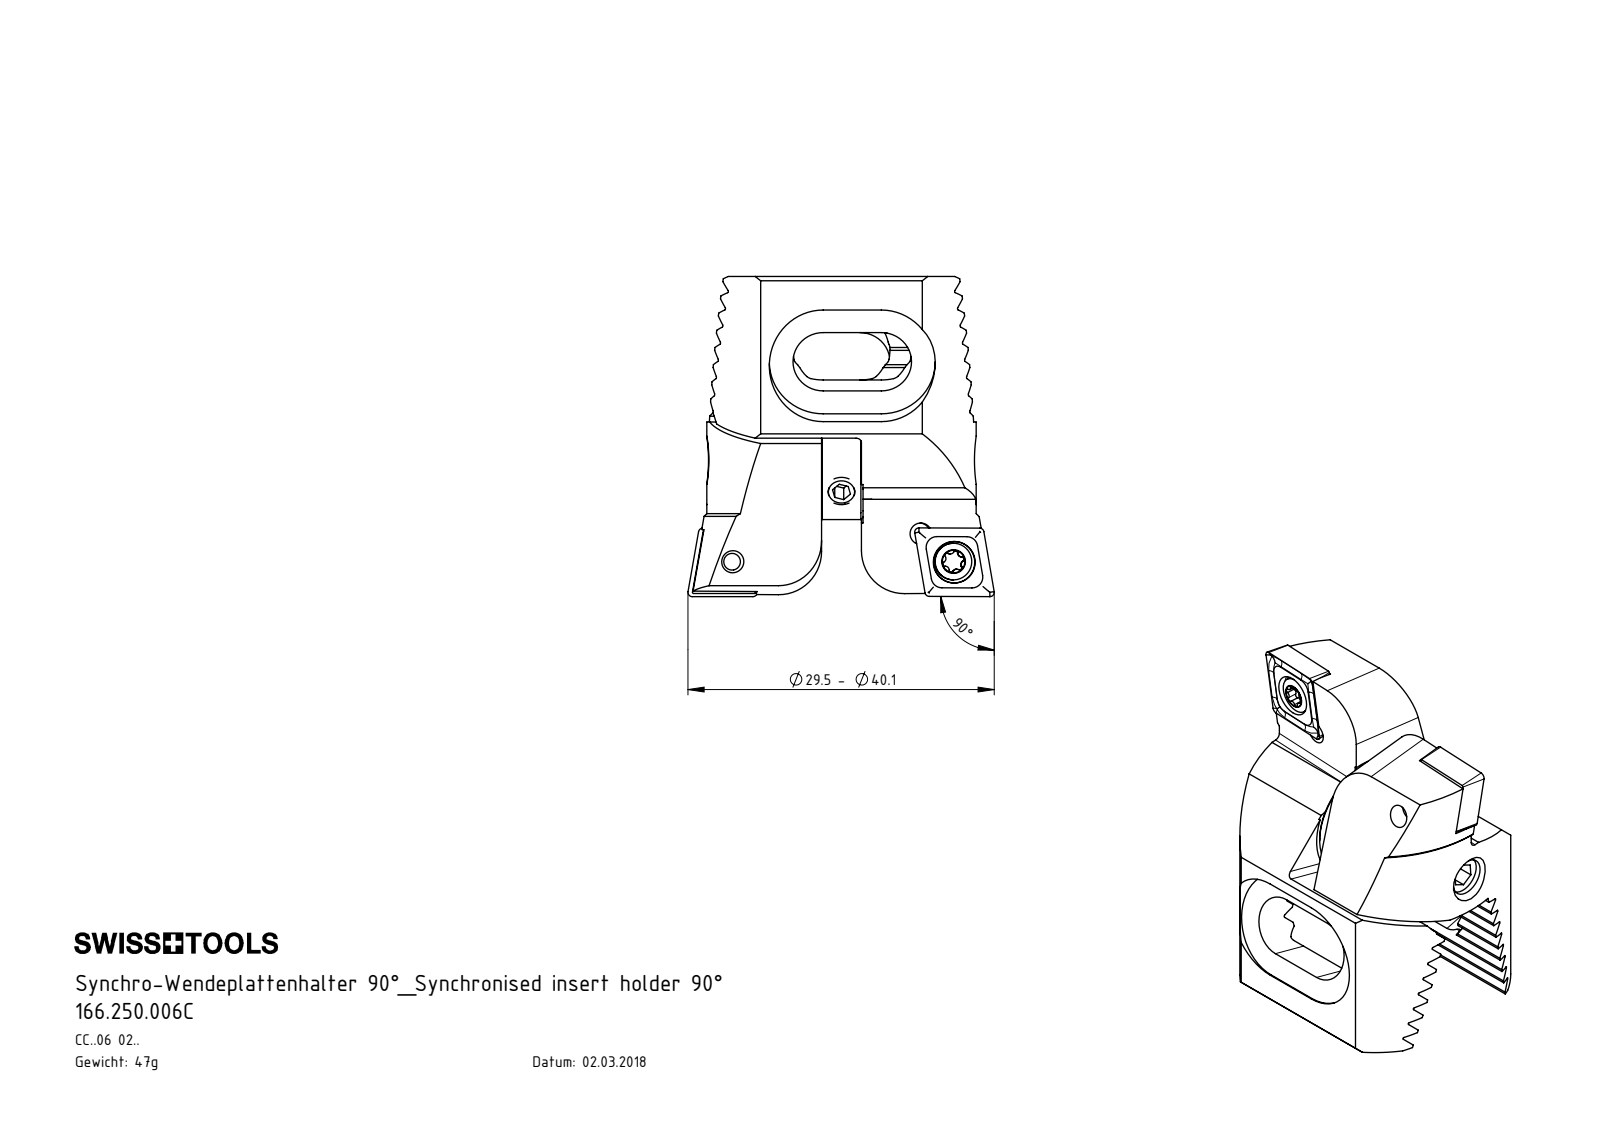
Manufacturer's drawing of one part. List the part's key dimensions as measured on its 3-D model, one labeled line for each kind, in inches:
Part name (STEP PRODUCT): ISO 4026 - M3 x 3; WCA-ER2.001.006_A; Z25-WCA.001.016_A; CCMT060204 (+4 more)
STEP written by: SolidWorks 2017 (CONFIG_CONTROL_DESIGN)
Units: inches
Bodies: 11 solids, 517 faces (205 planar, 172 cylindrical, 140 other)
Overall size (bounding box): 1.169 × 1.119 × 0.795
Volume: 0.357 in³ · Surface area: 8.37 in²
Round holes (diameter × count): ⌀0.039 ×3, ⌀0.098 ×3, ⌀0.079 ×2, ⌀0.081 ×2, ⌀0.11 ×2, ⌀0.152 ×2, ⌀0.138 ×1
Round bosses / shafts (diameter × count): ⌀0.118 ×4, ⌀0.134 ×2, ⌀0.098 ×2, ⌀0.433 ×1, ⌀0.157 ×1
Partial cylindrical surfaces — rounded edges, fillets, slot ends (radius × count): R0.005 ×16, R0.008 ×12, R0.014 ×10, R0.039 ×8, R0.02 ×4, R0.11 ×4, R0.197 ×4, R0.014 ×2
Main face-to-face distances: 0.056, 0.113, 0.169, 0.225, 0.124, 0.281, 0.337, 0.281, 0.157, 0.225
Hole centre spacings: 0.079, 0.157, 0.157, 0.161, 0.161, 0.283, 0.283, 0.294
